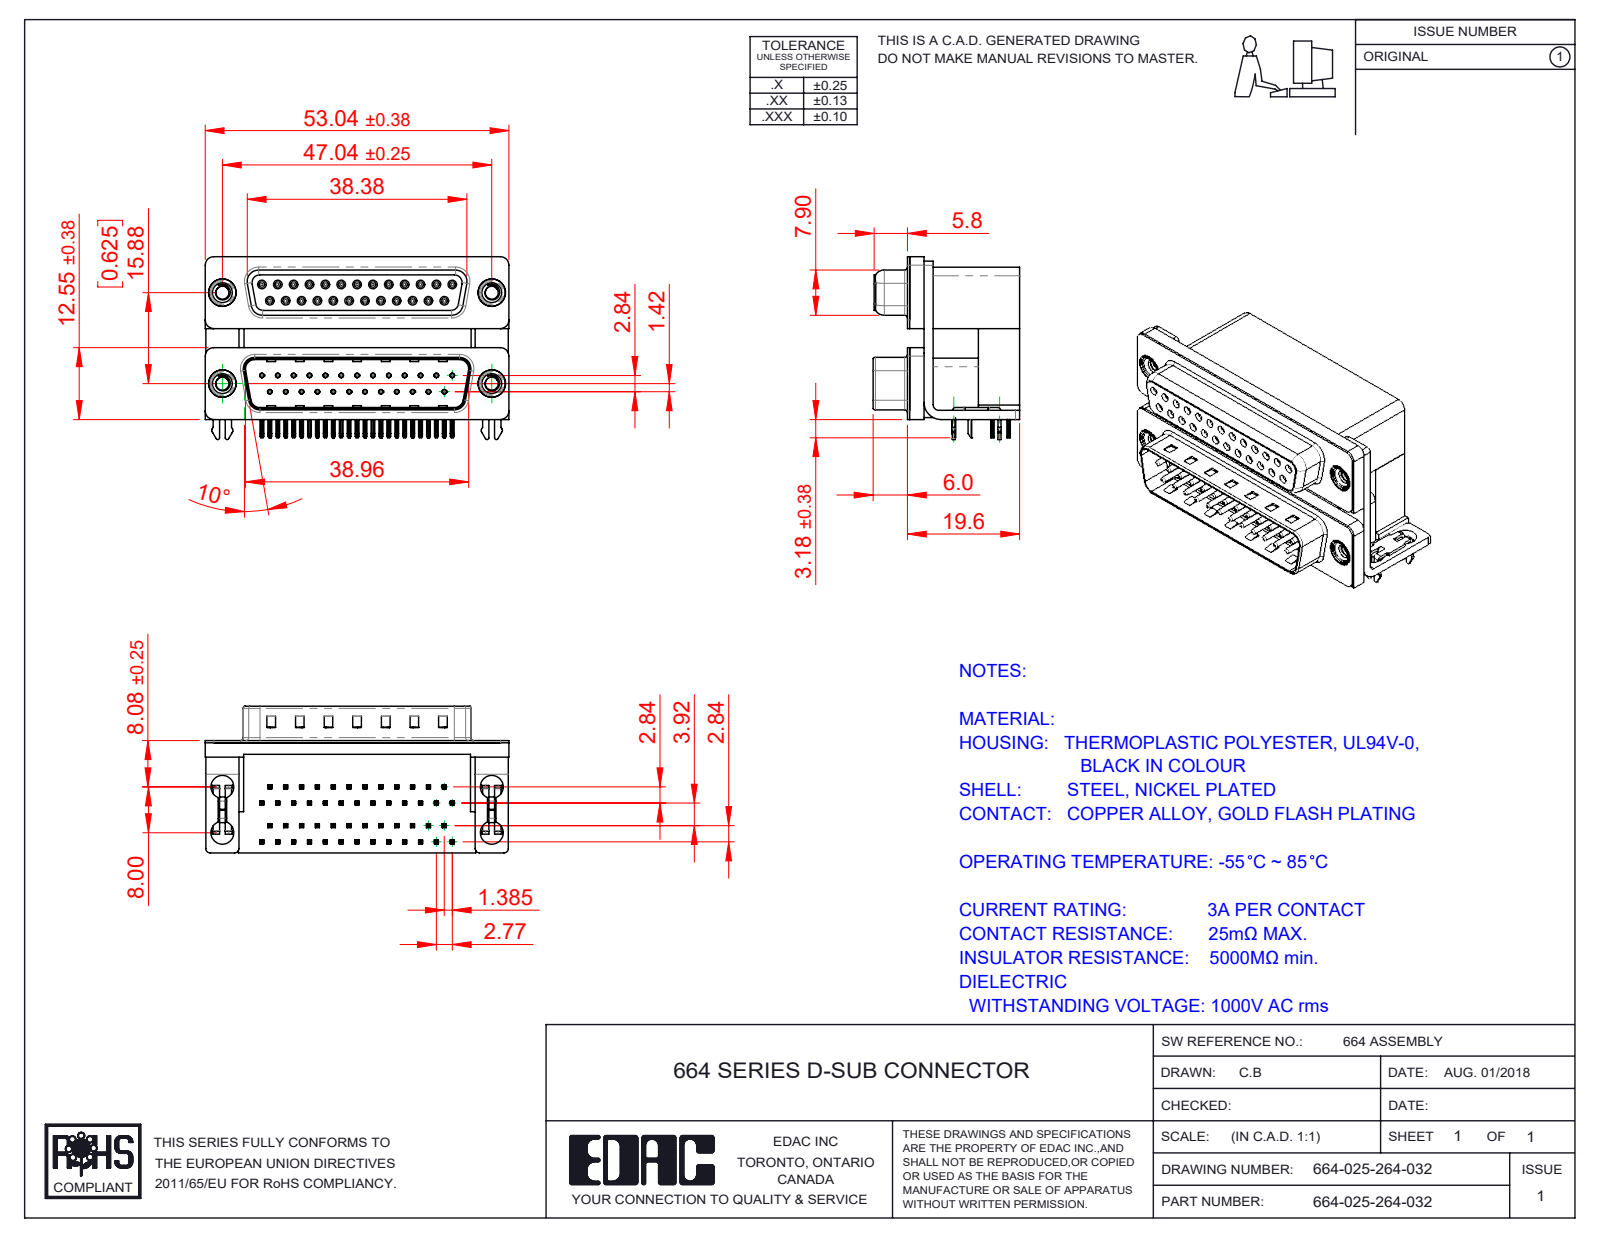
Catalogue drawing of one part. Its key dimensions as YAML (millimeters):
part_name: "664 Contact Bottom Lower; 664 Shell Receptacle_25 Contacts; 664 Contact Top Lower; 664-025-264-032 (+8 more)"
step_written_by: "SolidWorks 2020 (CONFIG_CONTROL_DESIGN)"
units: millimeters
bodies: {solids: 63, faces: 6355, planar: 3359, cylindrical: 1593, other: 1403}
overall_size: [53.04, 31.93, 25.6]
volume: 21551
surface_area: 23444
round_holes:
  - {diameter: 0.8, count: 50}
  - {diameter: 0.35, count: 25}
  - {diameter: 0.9, count: 25}
  - {diameter: 4, count: 8}
  - {diameter: 2.26, count: 4}
  - {diameter: 3.5, count: 4}
  - {diameter: 4.8, count: 4}
  - {diameter: 5, count: 4}
round_bosses_or_shafts:
  - {diameter: 1.2, count: 25}
  - {diameter: 0.75, count: 25}
  - {diameter: 4.9, count: 4}
  - {diameter: 4.75, count: 4}
  - {diameter: 3.9, count: 4}
partial_cylinders:
  - {radius: 0.1, count: 202}
  - {radius: 0.25, count: 110}
  - {radius: 0.15, count: 100}
  - {radius: 0.12, count: 50}
  - {radius: 0.35, count: 50}
  - {radius: 0.34, count: 25}
  - {radius: 0.5, count: 16}
  - {radius: 1.5, count: 13}
face_to_face_distances: [0.4, 19.2, 7.2, 12, 10.7, 16.7, 9.5, 2.5, 15.53, 26.23]
hole_center_spacings: [2.77, 3.16, 5.54, 8.31, 11.08, 13.85, 16.62, 5.03]
